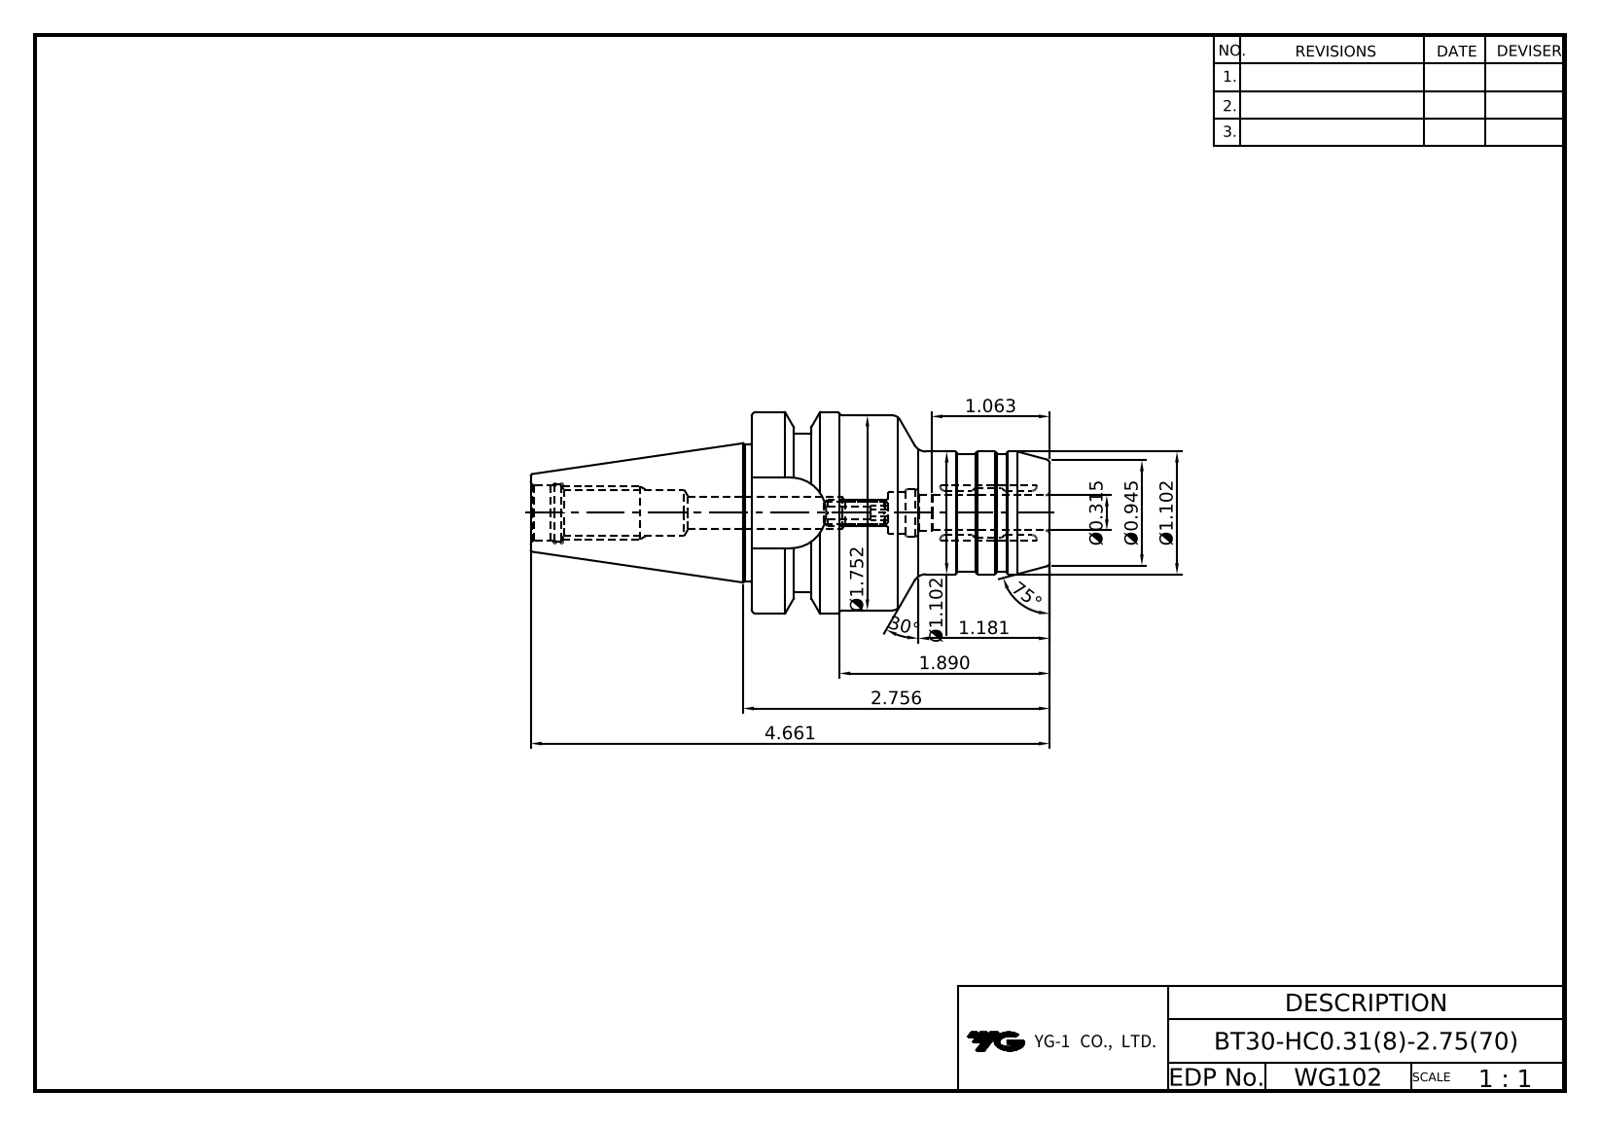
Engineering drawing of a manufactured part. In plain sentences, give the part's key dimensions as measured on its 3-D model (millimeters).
The part is named "LO-BT30ADB-HC8-70". Its 3-D file was written by "Autodesk Inventor 2022 (AUTOMOTIVE_DESIGN)". It is 1 solid with 95 faces: 20 planar, 39 cylindrical and 36 other. Overall it measures 118.4 by 46 by 46 millimeters. Its volume is 88 581 cubic millimeters and its surface area 18 262 square millimeters. Round holes: 4 of diameter 3.24, 4 of diameter 4, 1 of diameter 4.92, 1 of diameter 7.5, 1 of diameter 8, 1 of diameter 8.6, 1 of diameter 10.11, 1 of diameter 12.5, 1 of diameter 13.1. Round bosses or shafts: 1 of diameter 46, 1 of diameter 44.5, 1 of diameter 31.2, 1 of diameter 28, 1 of diameter 27. Partial cylindrical surfaces (rounded edges, fillets, slot ends): 1 of radius 8.05, 1 of radius 18. The main face-to-face distances are 68, 32.6, 13.6, 54.4, 4, 9.6, 58.4, 16.1, 50.4, 60.
